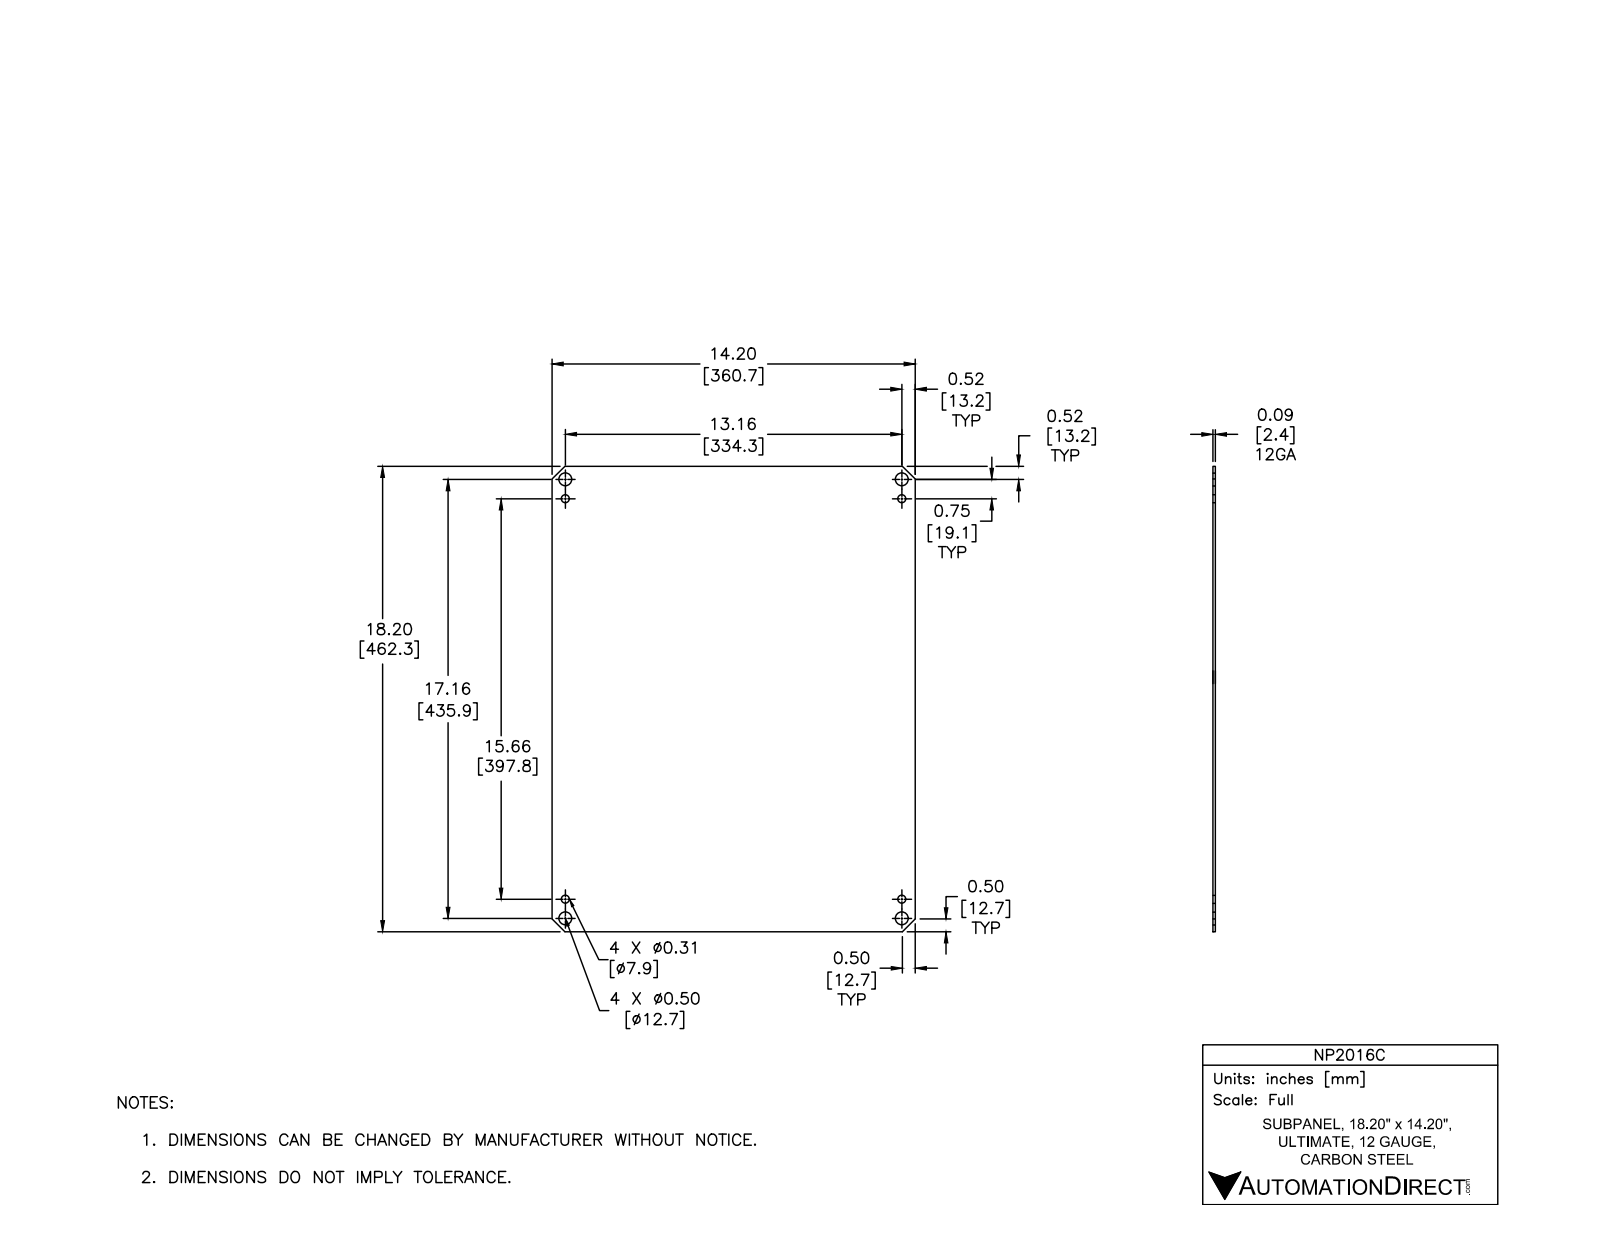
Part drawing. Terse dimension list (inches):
name: NP2016C
written by: Autodesk Inventor 2012 (AUTOMOTIVE_DESIGN)
unit: in
bodies: 1 solid, 18 faces (10 planar, 8 cylindrical, 0 other)
size: 18.2 × 14.2 × 0.094
volume: 24.08 in³; area: 520.6 in²
holes: 4× ⌀0.313, 4× ⌀0.5
face distances: 0.094, 14.2, 18.2, 22.2
hole spacings: 0.75, 13.16, 13.181, 16.41, 21.035, 15.66, 17.16, 20.455
